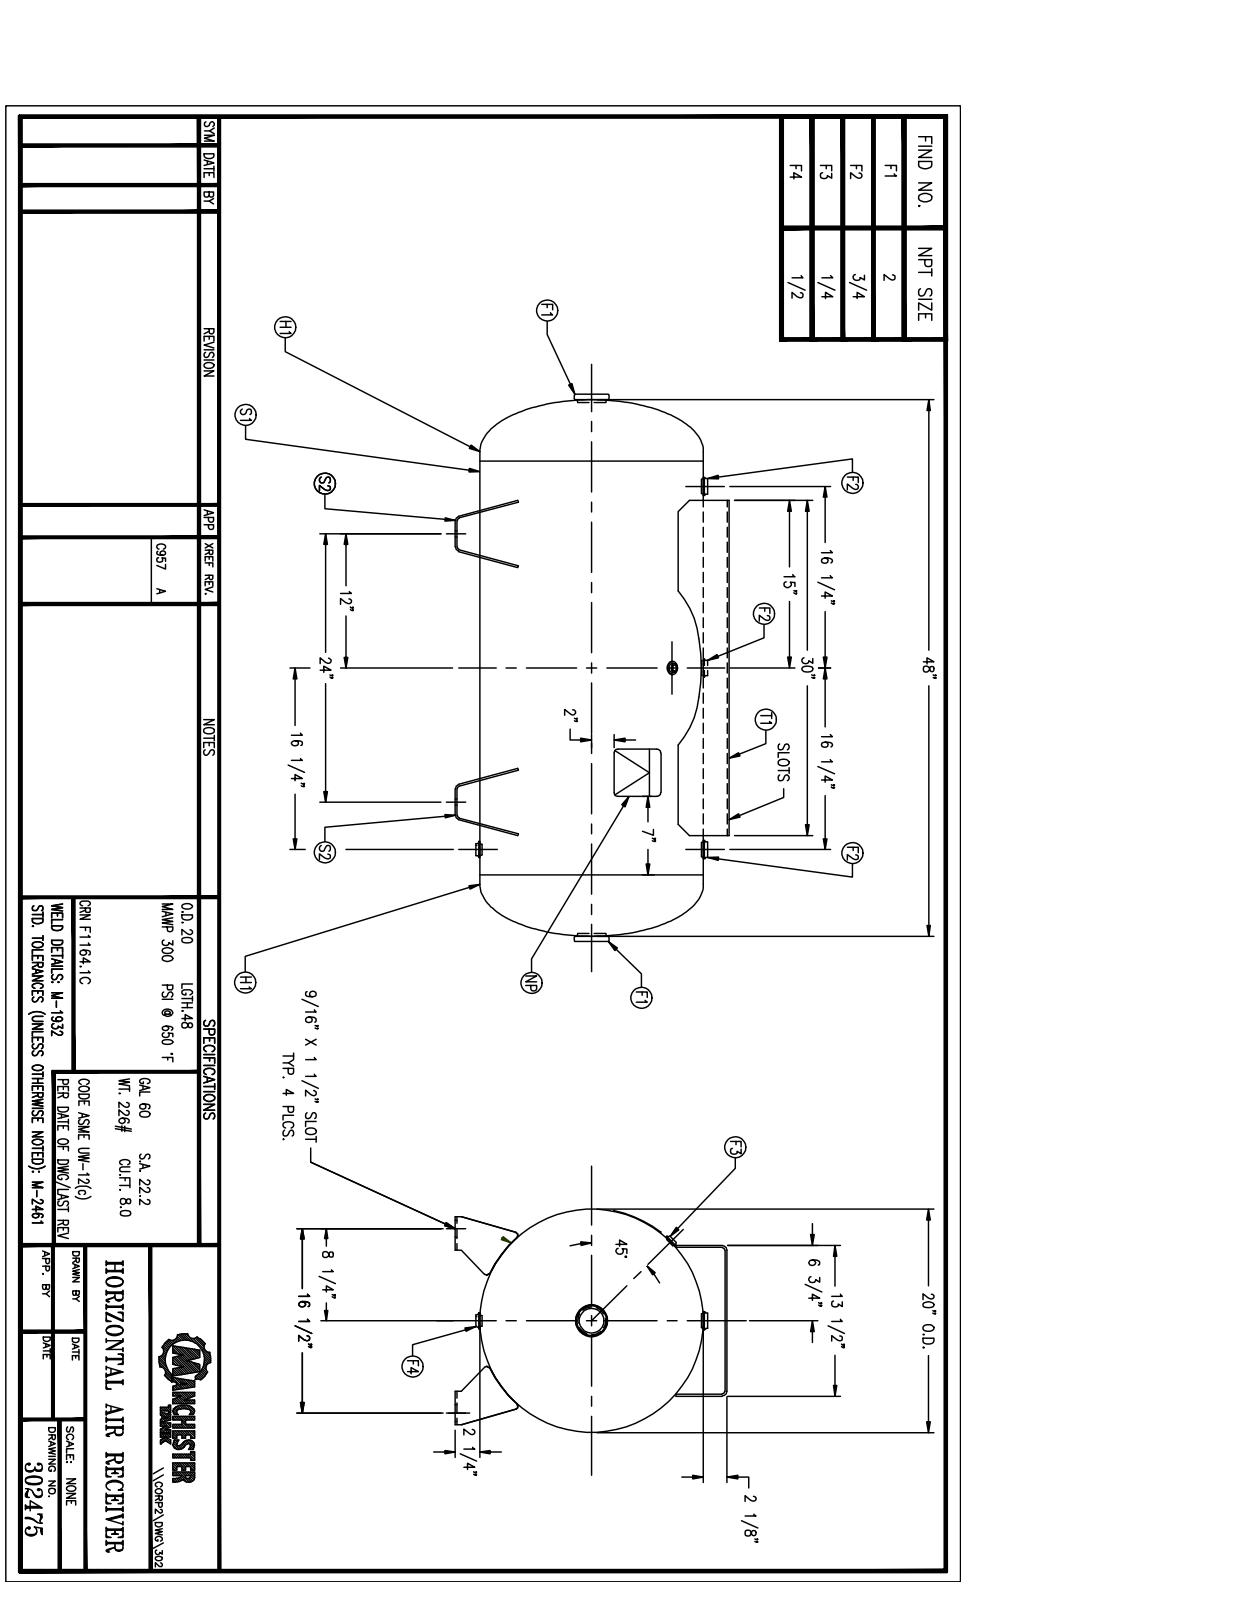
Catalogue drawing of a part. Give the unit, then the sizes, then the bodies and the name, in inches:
Units: inches
Overall size (bounding box): 49.156 × 24.358 × 20
Round holes (diameter × count): ⌀1.05 ×2, ⌀0.54 ×1, ⌀0.84 ×1, ⌀2.375 ×1, ⌀3 ×1, ⌀19 ×1, ⌀19.546 ×1
Round bosses / shafts (diameter × count): ⌀1.375 ×2, ⌀20 ×1, ⌀19.5 ×1, ⌀3 ×1, ⌀2.625 ×1, ⌀1.5 ×1, ⌀1.125 ×1
Partial cylindrical surfaces — rounded edges, fillets, slot ends (radius × count): R0.203 ×20, R0.25 ×20, R0.281 ×8, R10.125 ×6, R0.415 ×4, R0.429 ×2, R7.897 ×2, R10.06 ×1
Main face-to-face distances: 0.187, 13.313, 0.165, 13.5, 13.126, 23.184, 23.349, 0.164, 23.185, 23.019
Hole centre spacings: 16.25, 32.5
Bodies: 0 solids, 338 faces (143 planar, 139 cylindrical, 56 other)
Part name (STEP PRODUCT): 302475
STEP written by: SolidWorks 2011 (CONFIG_CONTROL_DESIGN)
